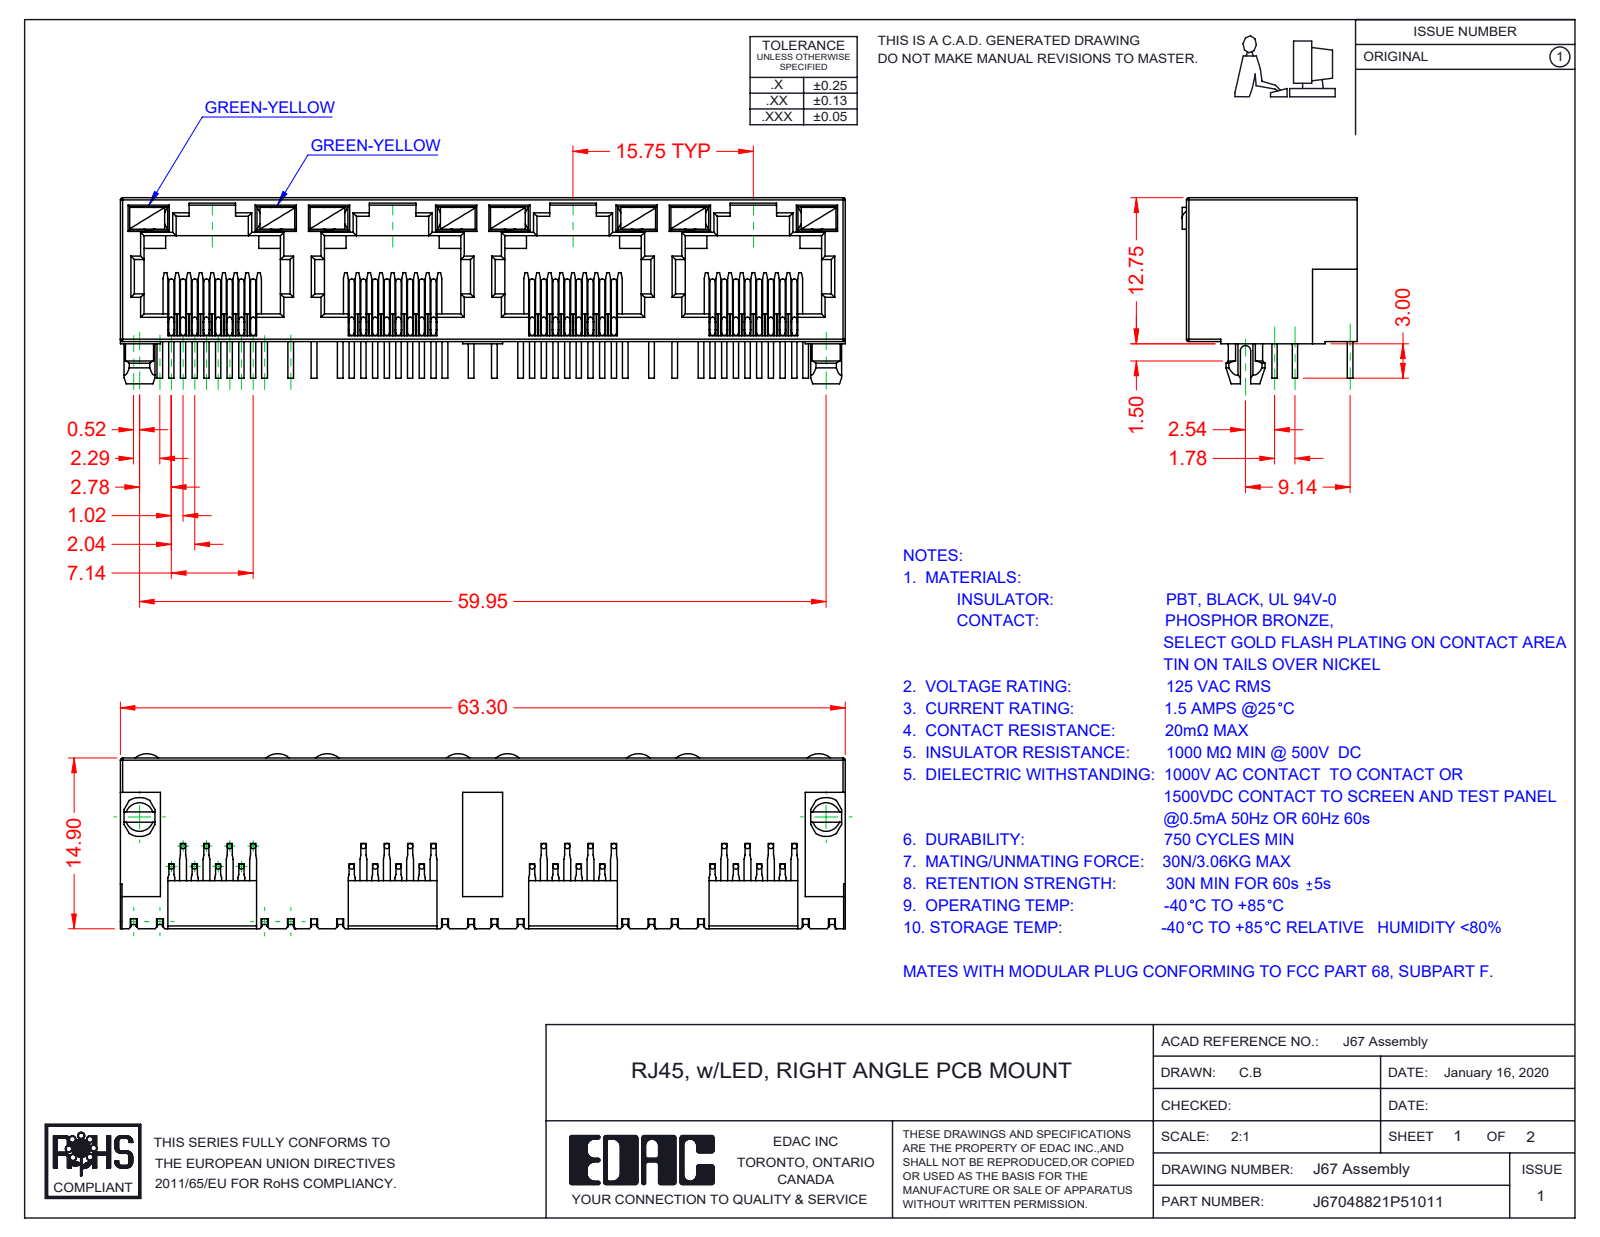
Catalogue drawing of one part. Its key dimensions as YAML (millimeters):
part_name: "67 Insulator; 67 LED RH_5-Green-Yellow; 67 LED LH_5-Green-Yellow; 67 Contacts (+1 more)"
step_written_by: "SolidWorks 2016 (CONFIG_CONTROL_DESIGN)"
units: millimeters
bodies: {solids: 41, faces: 2481, planar: 1781, cylindrical: 492, other: 208}
overall_size: [63.3, 16.25, 15.28]
volume: 5159
surface_area: 11573
round_bosses_or_shafts:
  - {diameter: 0.46, count: 96}
partial_cylinders:
  - {radius: 0.2, count: 66}
  - {radius: 0.3, count: 29}
  - {radius: 0.45, count: 9}
  - {radius: 1.55, count: 8}
  - {radius: 1.5, count: 2}
  - {radius: 1.7, count: 2}
  - {radius: 0.35, count: 1}
  - {radius: 1, count: 1}
face_to_face_distances: [0.5, 12.55, 1.89, 0.89, 10, 15.75, 1, 1.39, 11, 11.89]
